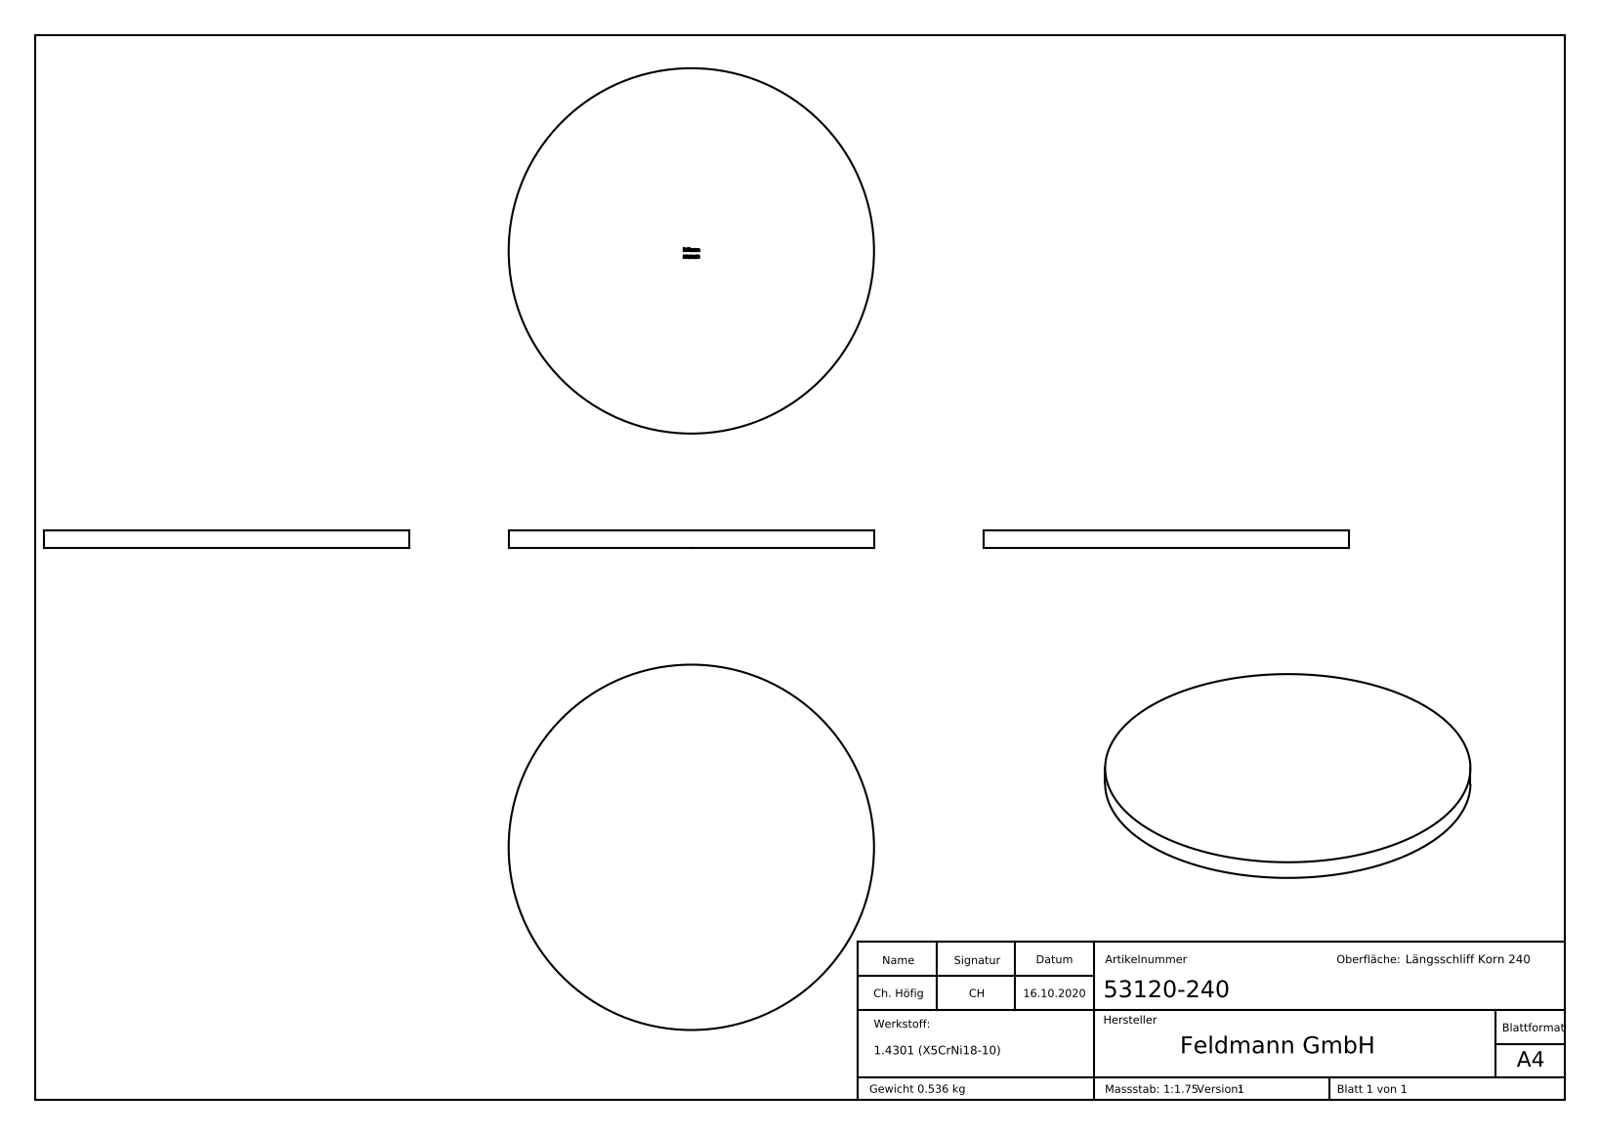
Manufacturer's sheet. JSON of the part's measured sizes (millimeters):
{"part_name": "53120-240", "step_written_by": "SolidWorks 2018 (CONFIG_CONTROL_DESIGN)", "units": "millimeters", "bodies": {"solids": 1, "faces": 225, "planar": 123, "cylindrical": 2, "other": 100}, "overall_size": [120, 120, 6], "volume_mm3": 67858, "surface_area_mm2": 24887, "round_bosses_or_shafts": [[120, 1]], "face_to_face_distances": [6, 5.9, 1.78, 0.83, 0.76, 2.45, 2.61, 0.53, 2.41, 0.99]}
